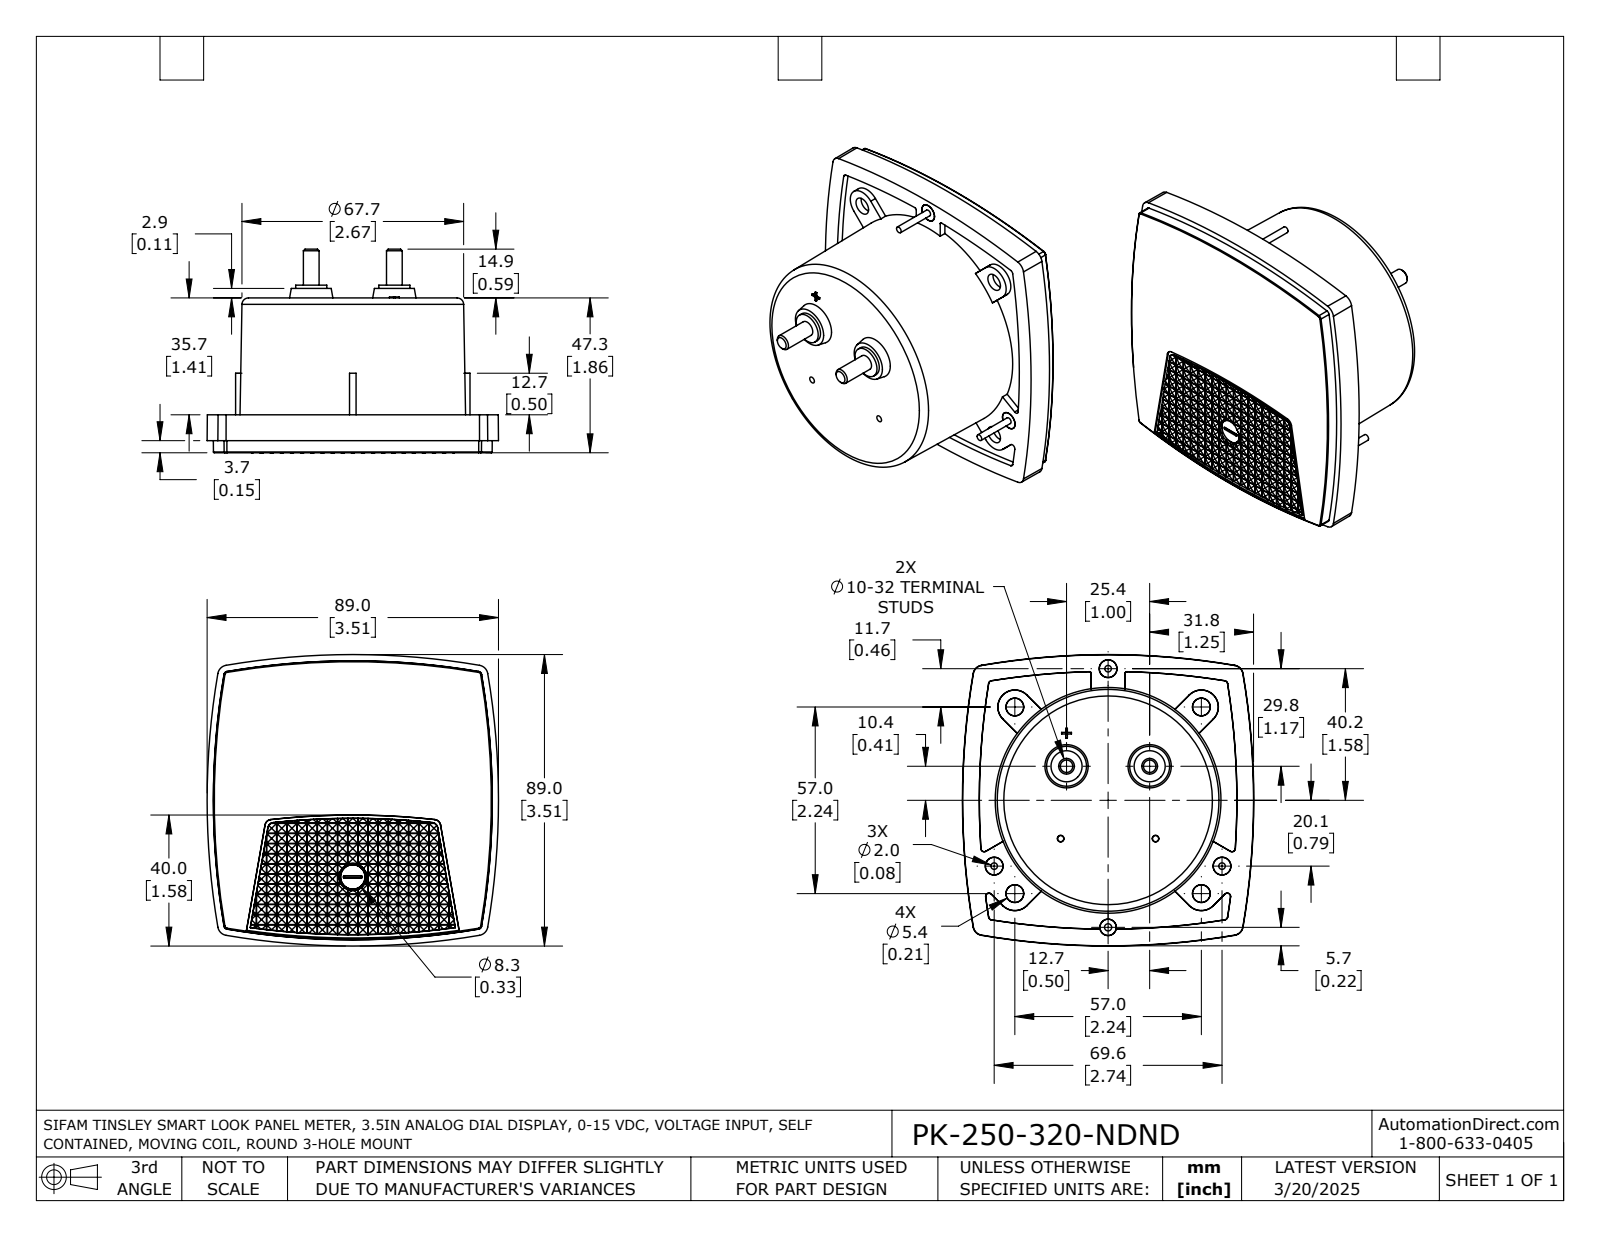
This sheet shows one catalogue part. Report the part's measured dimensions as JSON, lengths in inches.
{"part_name": "PK-250-320-NDND", "step_written_by": "SolidWorks 2021 (AUTOMOTIVE_DESIGN)", "units": "inches", "bodies": {"solids": 1, "faces": 1078, "planar": 950, "cylindrical": 23, "other": 105}, "overall_size": [3.505, 3.505, 2.453], "volume_in3": 12.99, "surface_area_in2": 44.29, "round_holes": [[0.087, 1]], "round_bosses_or_shafts": [[0.213, 3], [0.079, 3], [0.374, 2], [0.189, 2]], "partial_cylinders_radius": [[8.961, 1]], "face_to_face_distances": [1.862, 1.406, 0.457, 0.079, 1.484, 0.378, 0.024, 0.096, 0.072, 0.12]}
